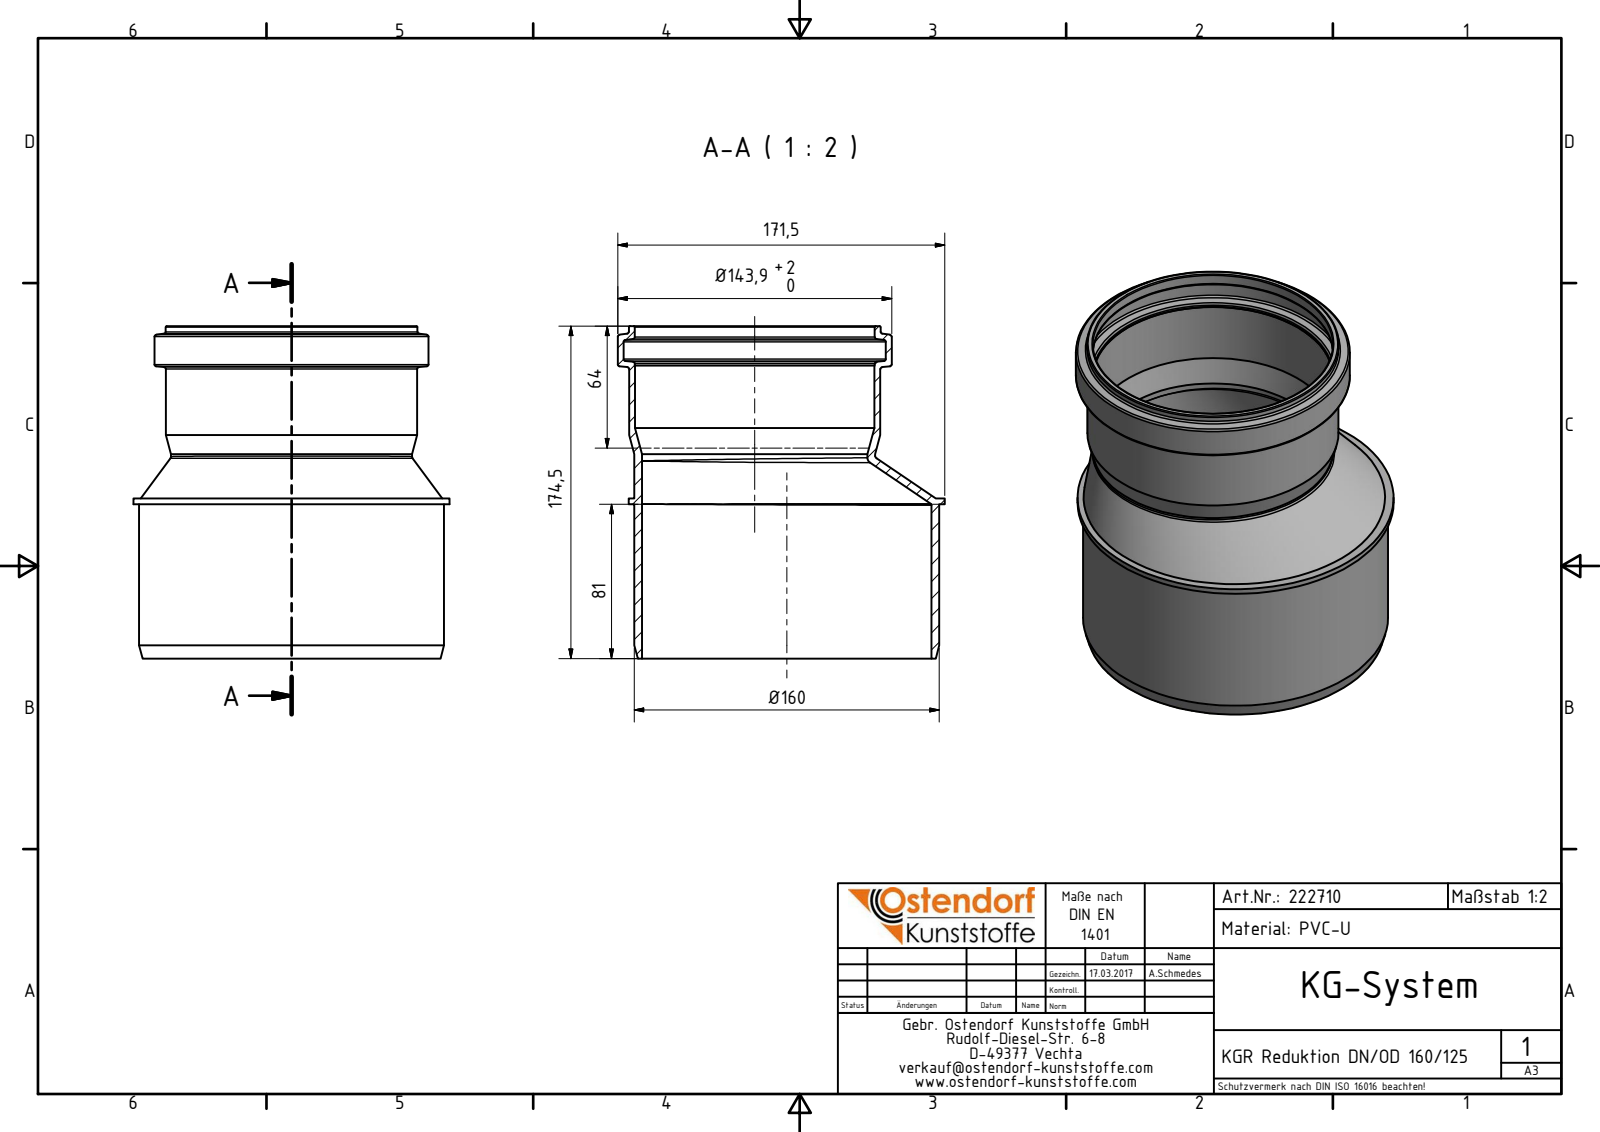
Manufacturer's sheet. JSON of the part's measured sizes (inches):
{"part_name": "222710 KGR Reduktion DN_OD 160_125", "step_written_by": "Autodesk Inventor 2016 (AUTOMOTIVE_DESIGN)", "units": "inches", "bodies": {"solids": 1, "faces": 39, "planar": 5, "cylindrical": 12, "other": 22}, "overall_size": [6.87, 6.763, 6.535], "volume_in3": 20.02, "surface_area_in2": 275.2, "round_holes": [[4.659, 1], [4.949, 1], [4.961, 1], [5.421, 1], [5.984, 1]], "round_bosses_or_shafts": [[6.535, 1], [6.307, 1], [5.665, 1], [5.205, 1], [5.193, 1], [4.982, 1]], "face_to_face_distances": [0.118, 3.189, 3.307, 6.87, 3.681, 3.563, 6.053, 2.864, 2.746, 0.817], "hole_center_spacings": [0.662]}
